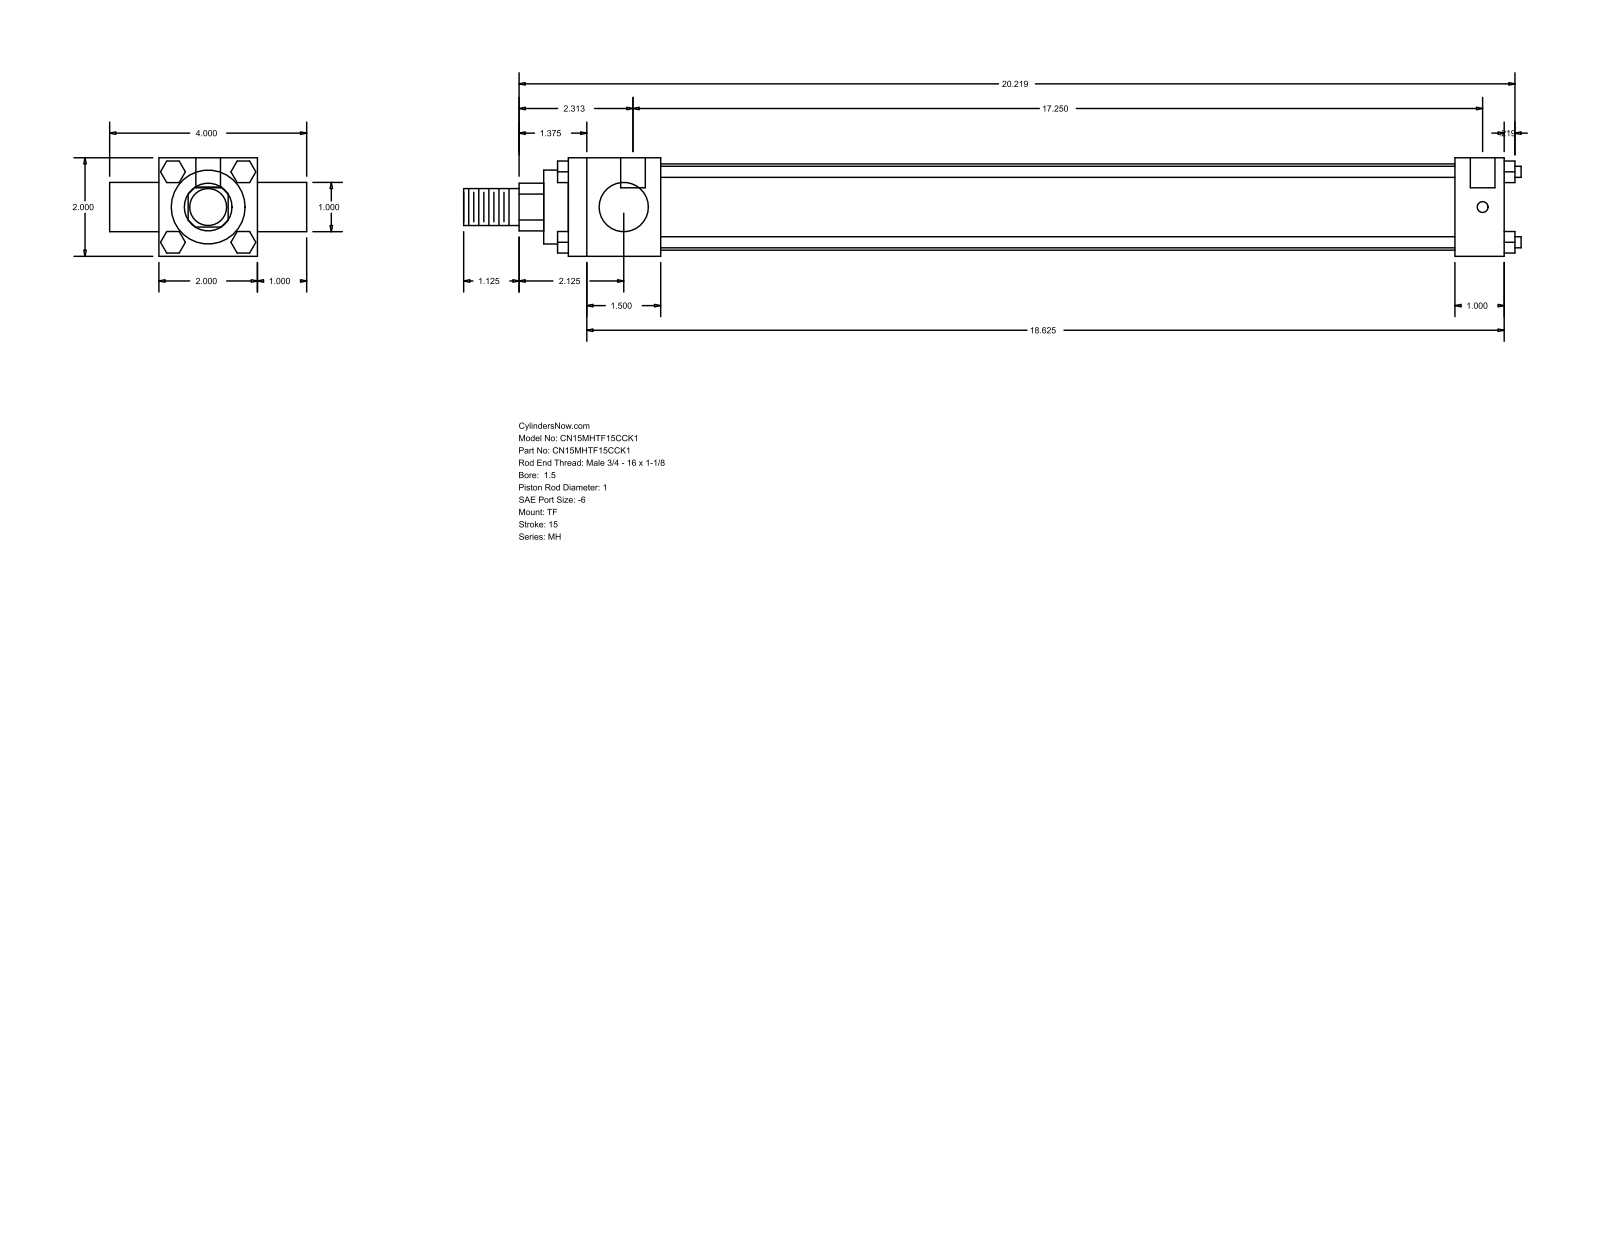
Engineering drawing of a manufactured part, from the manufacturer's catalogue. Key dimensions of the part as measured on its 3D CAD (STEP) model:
Part name (STEP PRODUCT): MH_TF__0150_1
STEP written by: GSSL Pune (CONFIG_CONTROL_DESIGN)
Units: millimetres
Bodies: 0 solids, 120 faces (92 planar, 28 cylindrical, 0 other)
Overall size (bounding box): 545.31 × 101.6 × 50.8
Round holes (diameter × count): ⌀5.56 ×3, ⌀12.7 ×2
Round bosses / shafts (diameter × count): ⌀5.71 ×4, ⌀25.4 ×2, ⌀44.45 ×1, ⌀38.1 ×1, ⌀19.05 ×1
Partial cylindrical surfaces — rounded edges, fillets, slot ends (radius × count): R12.29 ×1
Main face-to-face distances: 50.8, 25.4, 482.6, 76.2, 47.63, 434.97, 457.2, 409.57, 101.6, 12.7
Hole centre spacings: 3.18, 438.15, 441.33
